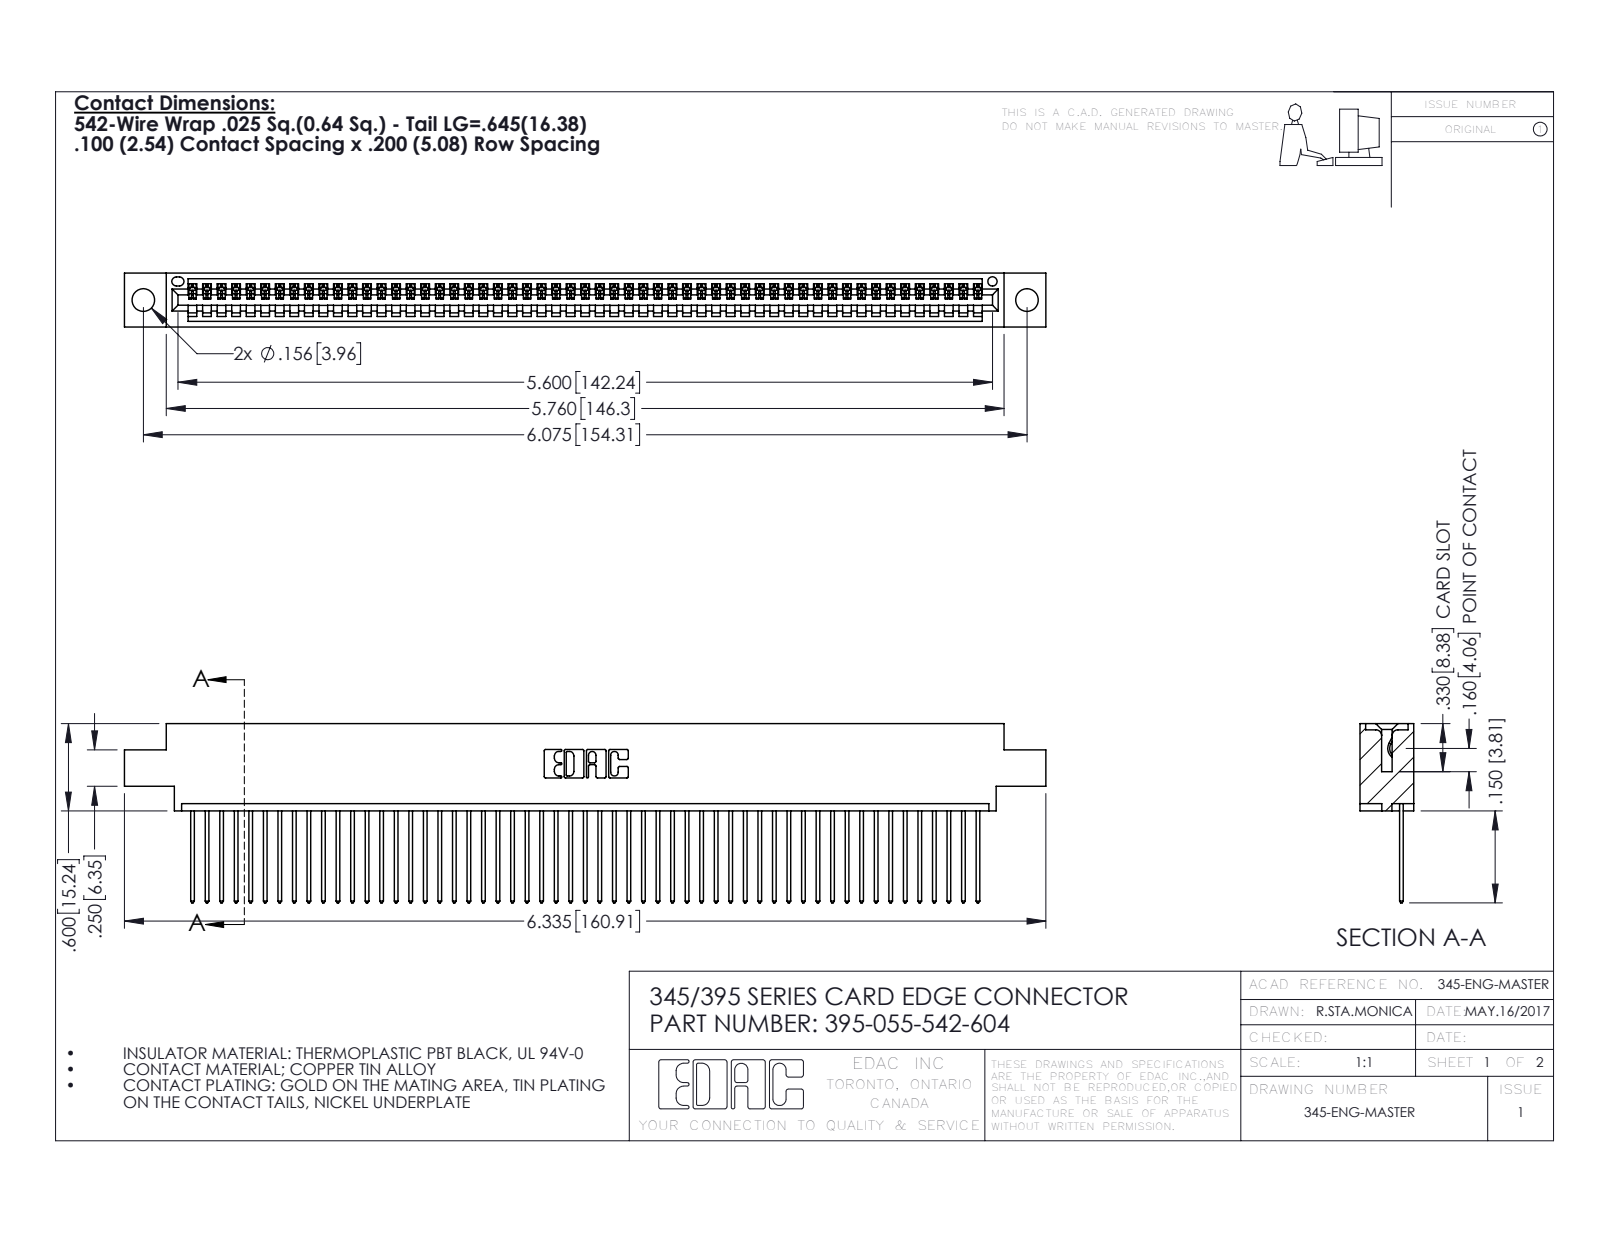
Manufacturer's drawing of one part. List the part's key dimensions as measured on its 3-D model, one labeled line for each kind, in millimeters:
Part name (STEP PRODUCT): 395-055-542-604; 345-292-001_345-293-142; 345 Part_0.170 Offset - 0.156 Dia-TH
STEP written by: SolidWorks 2016 (CONFIG_CONTROL_DESIGN)
Units: millimetres
Bodies: 56 solids, 3320 faces (2284 planar, 1036 cylindrical, 0 other)
Overall size (bounding box): 160.9 × 31.3 × 9.4
Volume: 15 300 mm³ · Surface area: 21 230 mm²
Round holes (diameter × count): ⌀4 ×2, ⌀1.6 ×1
Partial cylindrical surfaces — rounded edges, fillets, slot ends (radius × count): R0.2 ×110, R0.3 ×110, R0.3 ×22, R0.2 ×6, R0.8 ×6, R0.7 ×3, R0.8 ×2, R1 ×2
Main face-to-face distances: 1.8, 7.6, 9.4, 2.5, 6.9, 0.6, 5.1, 5.7, 4.4, 3.8
Hole centre spacings: 6.9, 148.3, 154.3
